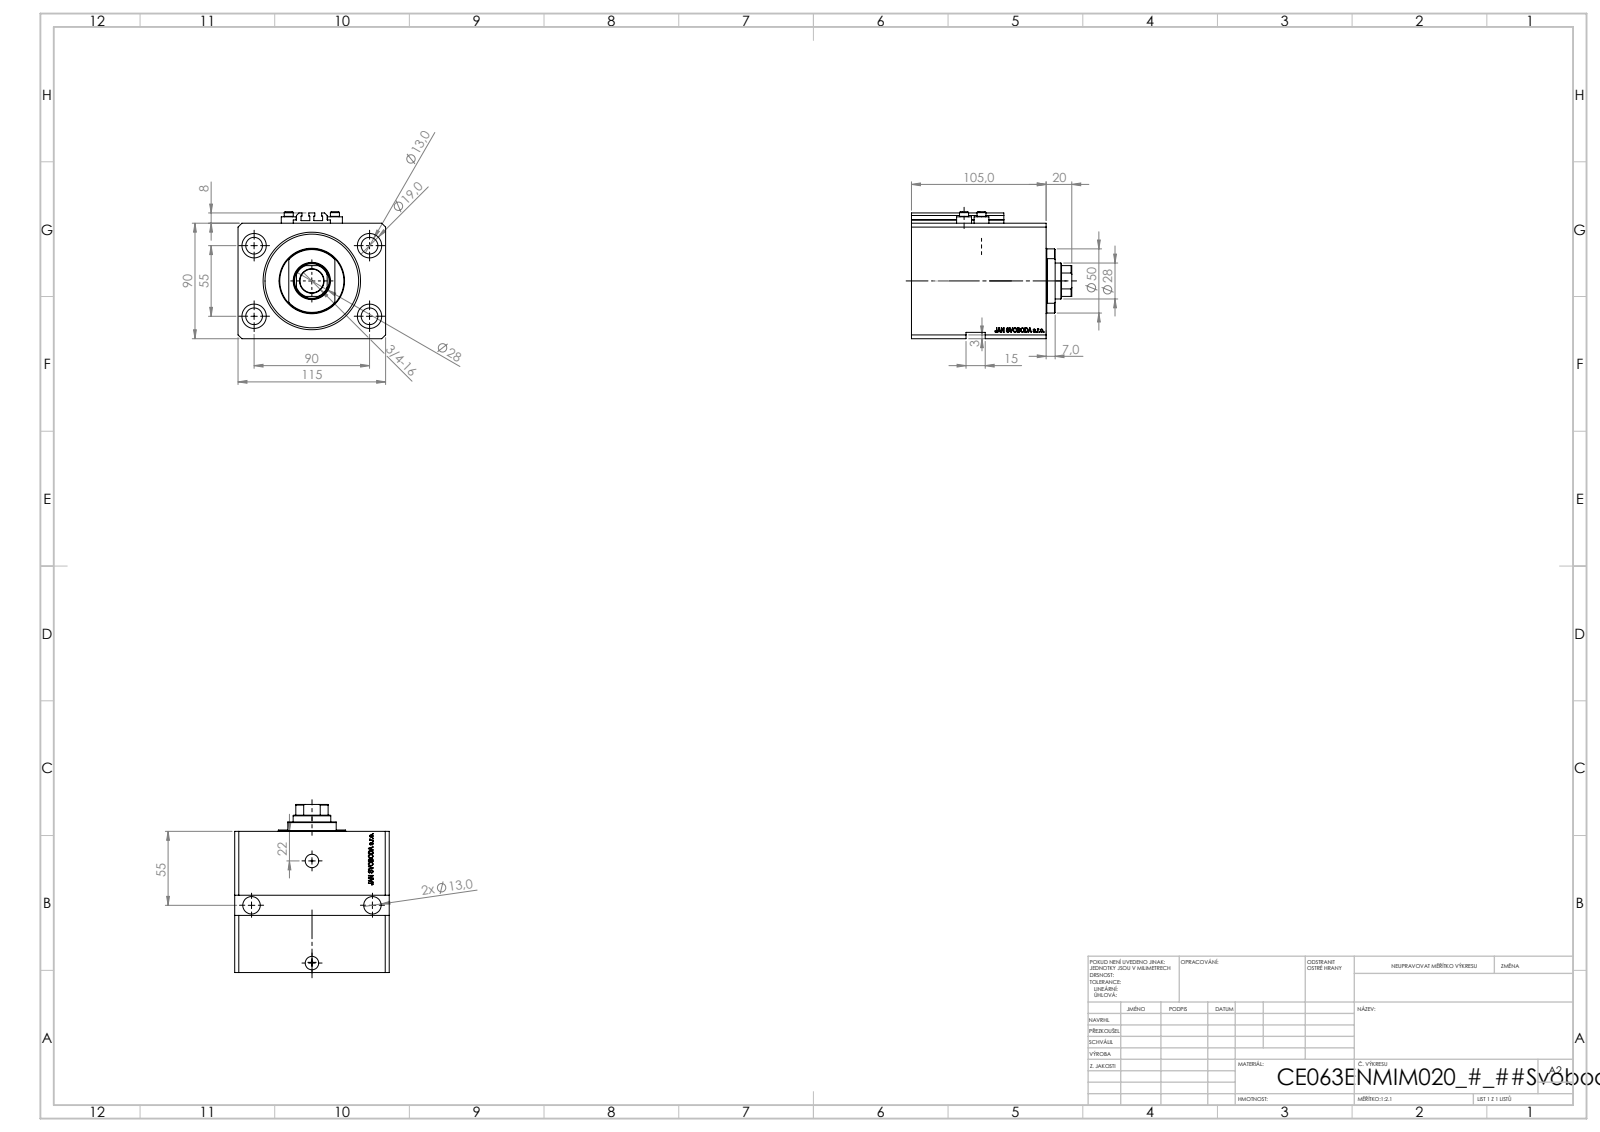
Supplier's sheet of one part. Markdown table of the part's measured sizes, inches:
| quantity | value |
| --- | --- |
| part name | V250CE_C_VCP; V250CE_VC_E; ALLEN BOLT V250CE; V250CE_E_Body |
| STEP written by | SolidWorks 2019 (CONFIG_CONTROL_DESIGN) |
| units | inches |
| bodies | 8 solids, 1107 faces (543 planar, 126 cylindrical, 438 other) |
| overall size | 4.921 × 4.528 × 3.898 |
| volume | 58.25 in³ |
| surface area | 238.6 in² |
| round holes (diameter × count) | 0.512 × 6, 0.049 × 4, 0.157 × 4, 0.748 × 4, 0.394 × 2, 0.518 × 2, 0.787 × 2, 0.728 × 1, 1.102 × 1, 2.48 × 1, 2.992 × 1 |
| round bosses / shafts (diameter × count) | 0.457 × 4, 0.276 × 4, 1.969 × 1 |
| partial cylindrical surfaces (radius × count) | 0.008 × 10, 0.531 × 1 |
| main face-to-face distances | 3.543, 0.787, 4.528, 3.346, 4.134, 3.429, 0.705, 2.642, 1.575, 2.559 |
| hole center spacings | 2.076, 2.165, 3.543, 0.535, 1.078, 1.12, 1.324, 1.417 |
